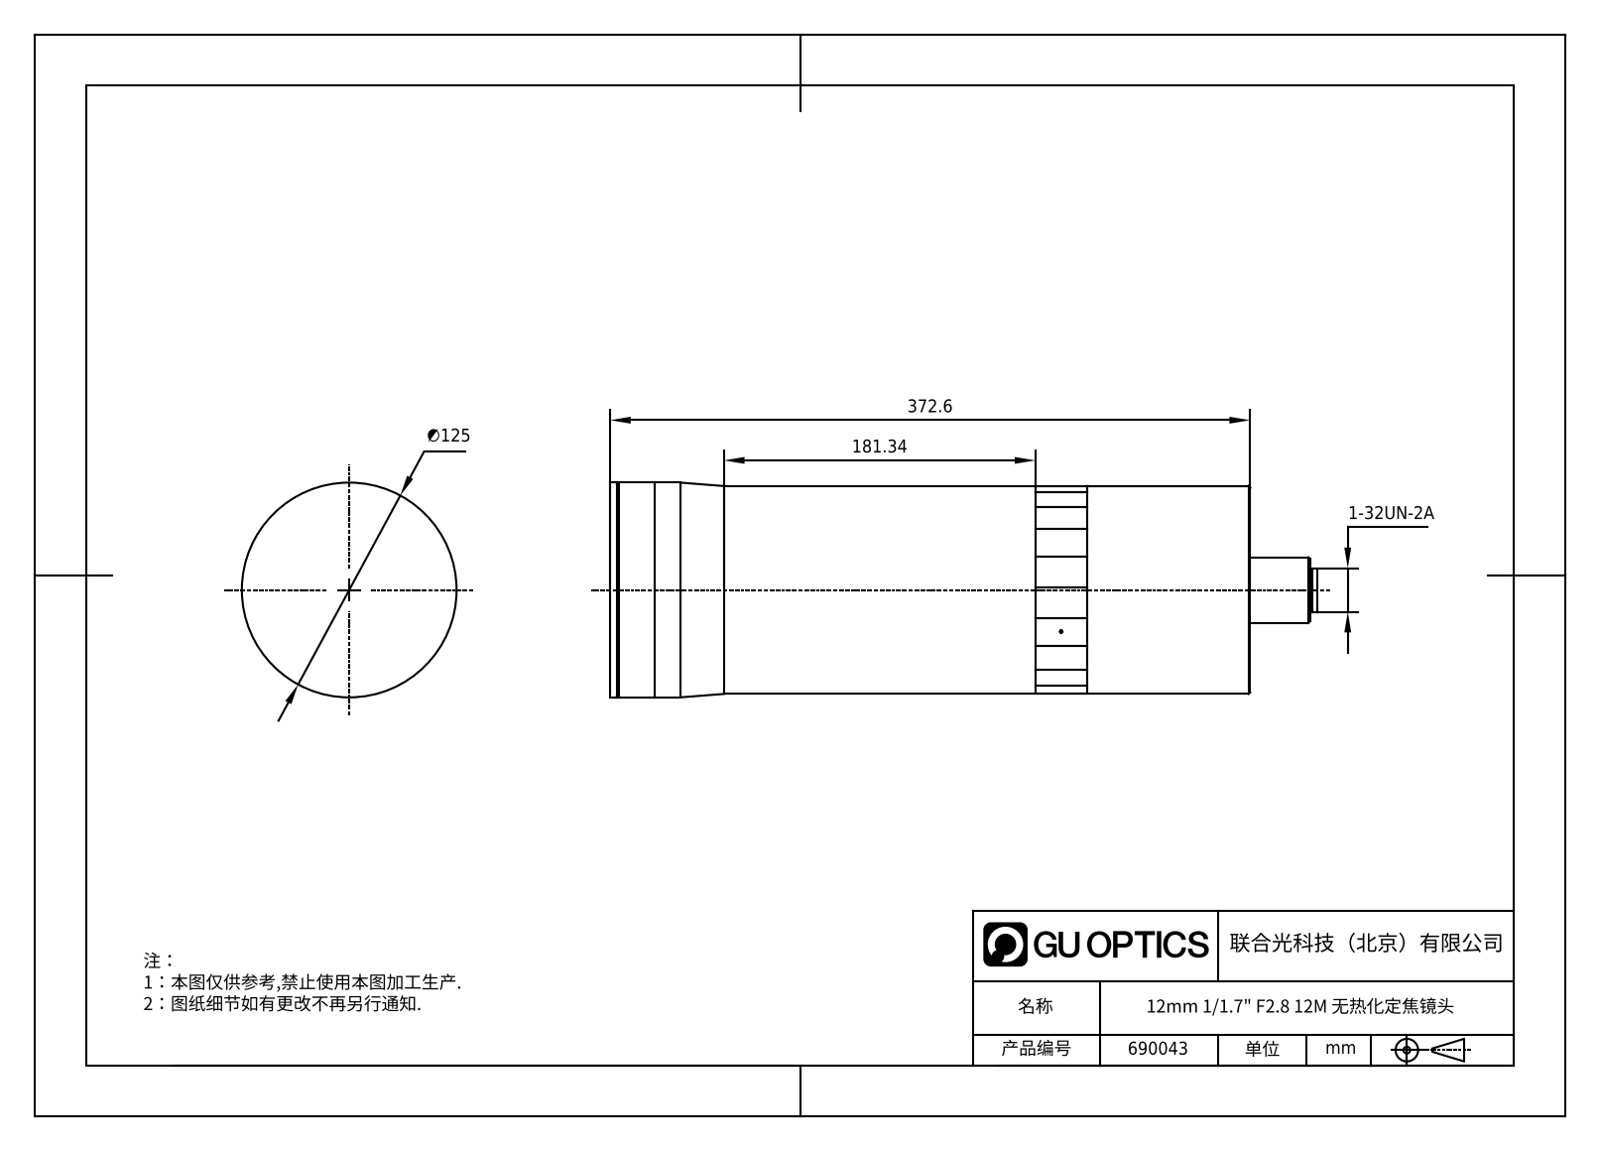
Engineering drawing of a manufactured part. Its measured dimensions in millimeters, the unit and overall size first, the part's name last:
Units: millimetres
Overall size (bounding box): 425.14 × 129 × 129
Round holes (diameter × count): ⌀1.6 ×13, ⌀2.05 ×2, ⌀3 ×1, ⌀19 ×1, ⌀21 ×1, ⌀21 ×1, ⌀22 ×1, ⌀33 ×1, ⌀36 ×1, ⌀79 ×1, ⌀82 ×1, ⌀84 ×1
Round bosses / shafts (diameter × count): ⌀125 ×1, ⌀122.2 ×1, ⌀121 ×1, ⌀115 ×1, ⌀105.8 ×1, ⌀90 ×1, ⌀38 ×1, ⌀25.4 ×1
Partial cylindrical surfaces — rounded edges, fillets, slot ends (radius × count): R0.5 ×32, R75 ×21, R1.5 ×4
Main face-to-face distances: 2, 11.5, 13.5, 4, 372.6, 370.6, 368.6, 349.49, 362.99, 360.99
Hole centre spacings: 40.75, 53.25, 98.39, 75.3, 75.31, 106.49, 106.5, 18
Volume: 958 046 mm³ · Surface area: 675 496 mm²
Bodies: 17 solids, 427 faces (92 planar, 262 cylindrical, 73 other)
Part name (STEP PRODUCT): C口; product-name; 前盖; 消光筒 (+8 more)
STEP written by: SolidWorks 2016 (AUTOMOTIVE_DESIGN)
